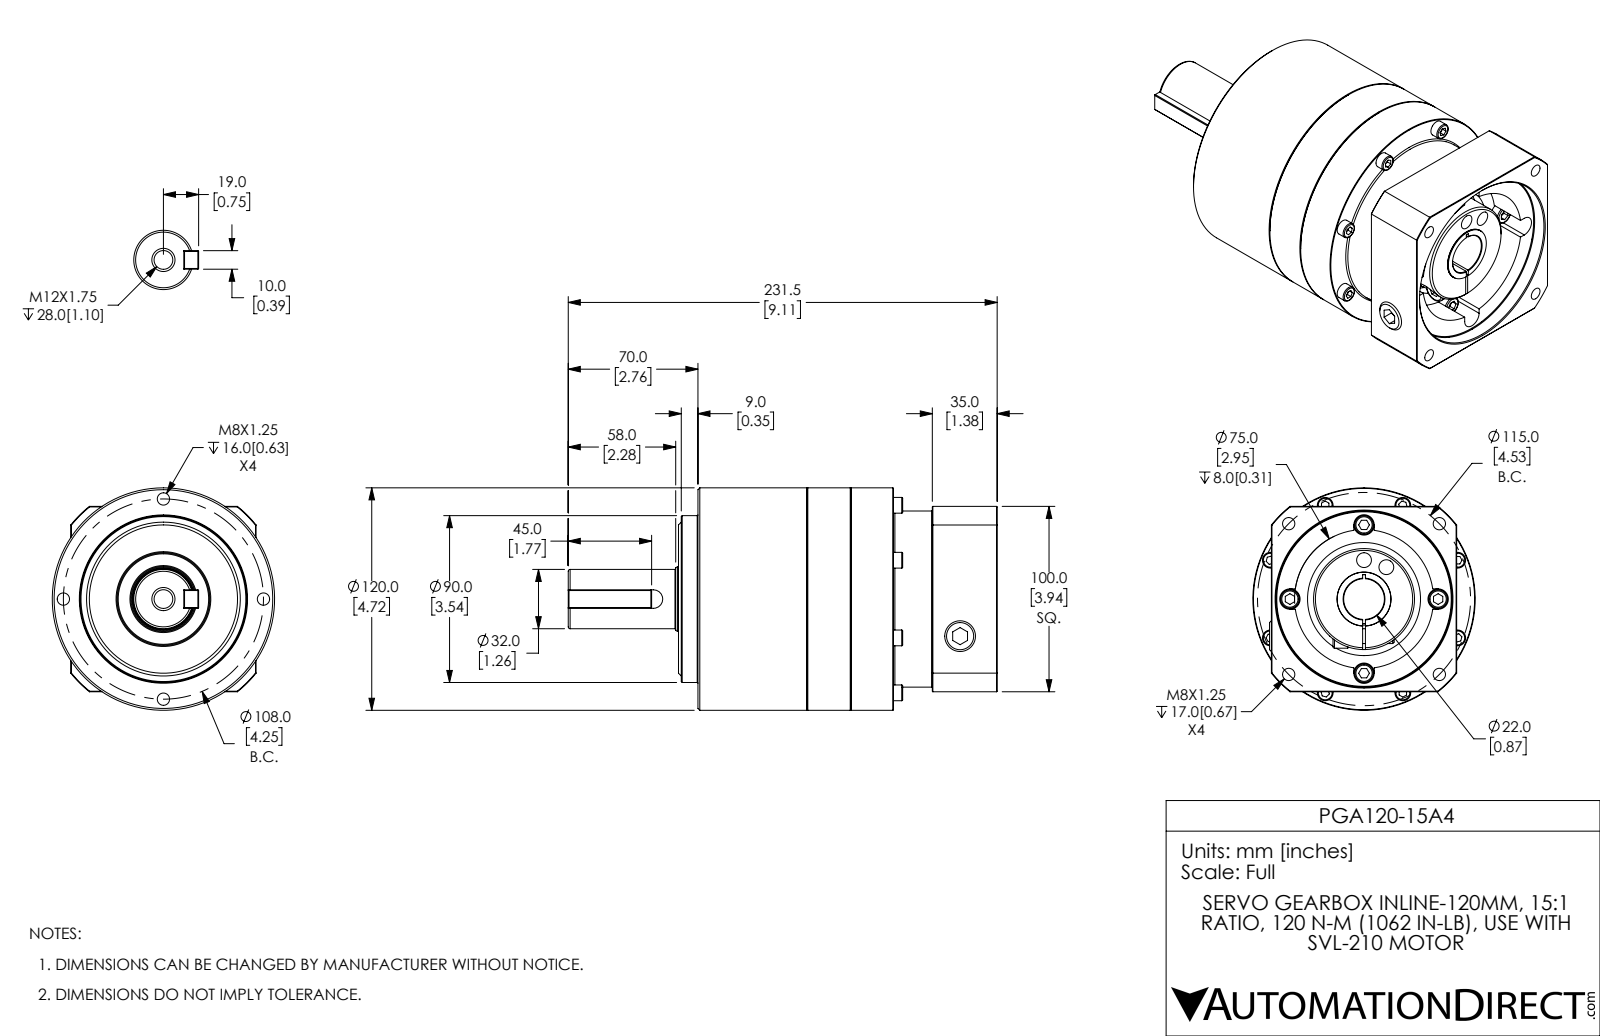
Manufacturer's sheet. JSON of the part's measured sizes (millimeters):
{"part_name": "PGA120-15A4", "step_written_by": "SolidWorks 2019 (CONFIG_CONTROL_DESIGN)", "units": "millimeters", "bodies": {"solids": 1, "faces": 431, "planar": 184, "cylindrical": 105, "other": 142}, "overall_size": [231.5, 120, 120], "volume_mm3": 1645000, "surface_area_mm2": 125909, "round_holes": [[6.65, 8], [11, 4], [8, 2], [8.8, 1], [10.11, 1], [14.25, 1], [22, 1], [61, 1], [75, 1], [95, 1]], "round_bosses_or_shafts": [[8.5, 8], [10, 4], [120, 1], [90, 1], [54.5, 1], [35, 1], [32, 1], [29, 1]], "partial_cylinders_radius": [[3.32, 1], [5, 1], [7, 1], [64, 1]], "face_to_face_distances": [100, 28, 10.5, 105.5, 116, 21, 126.5, 137, 7, 8], "hole_center_spacings": [40.67, 42.79, 67.2, 90.33, 103.02, 14, 40, 54]}
